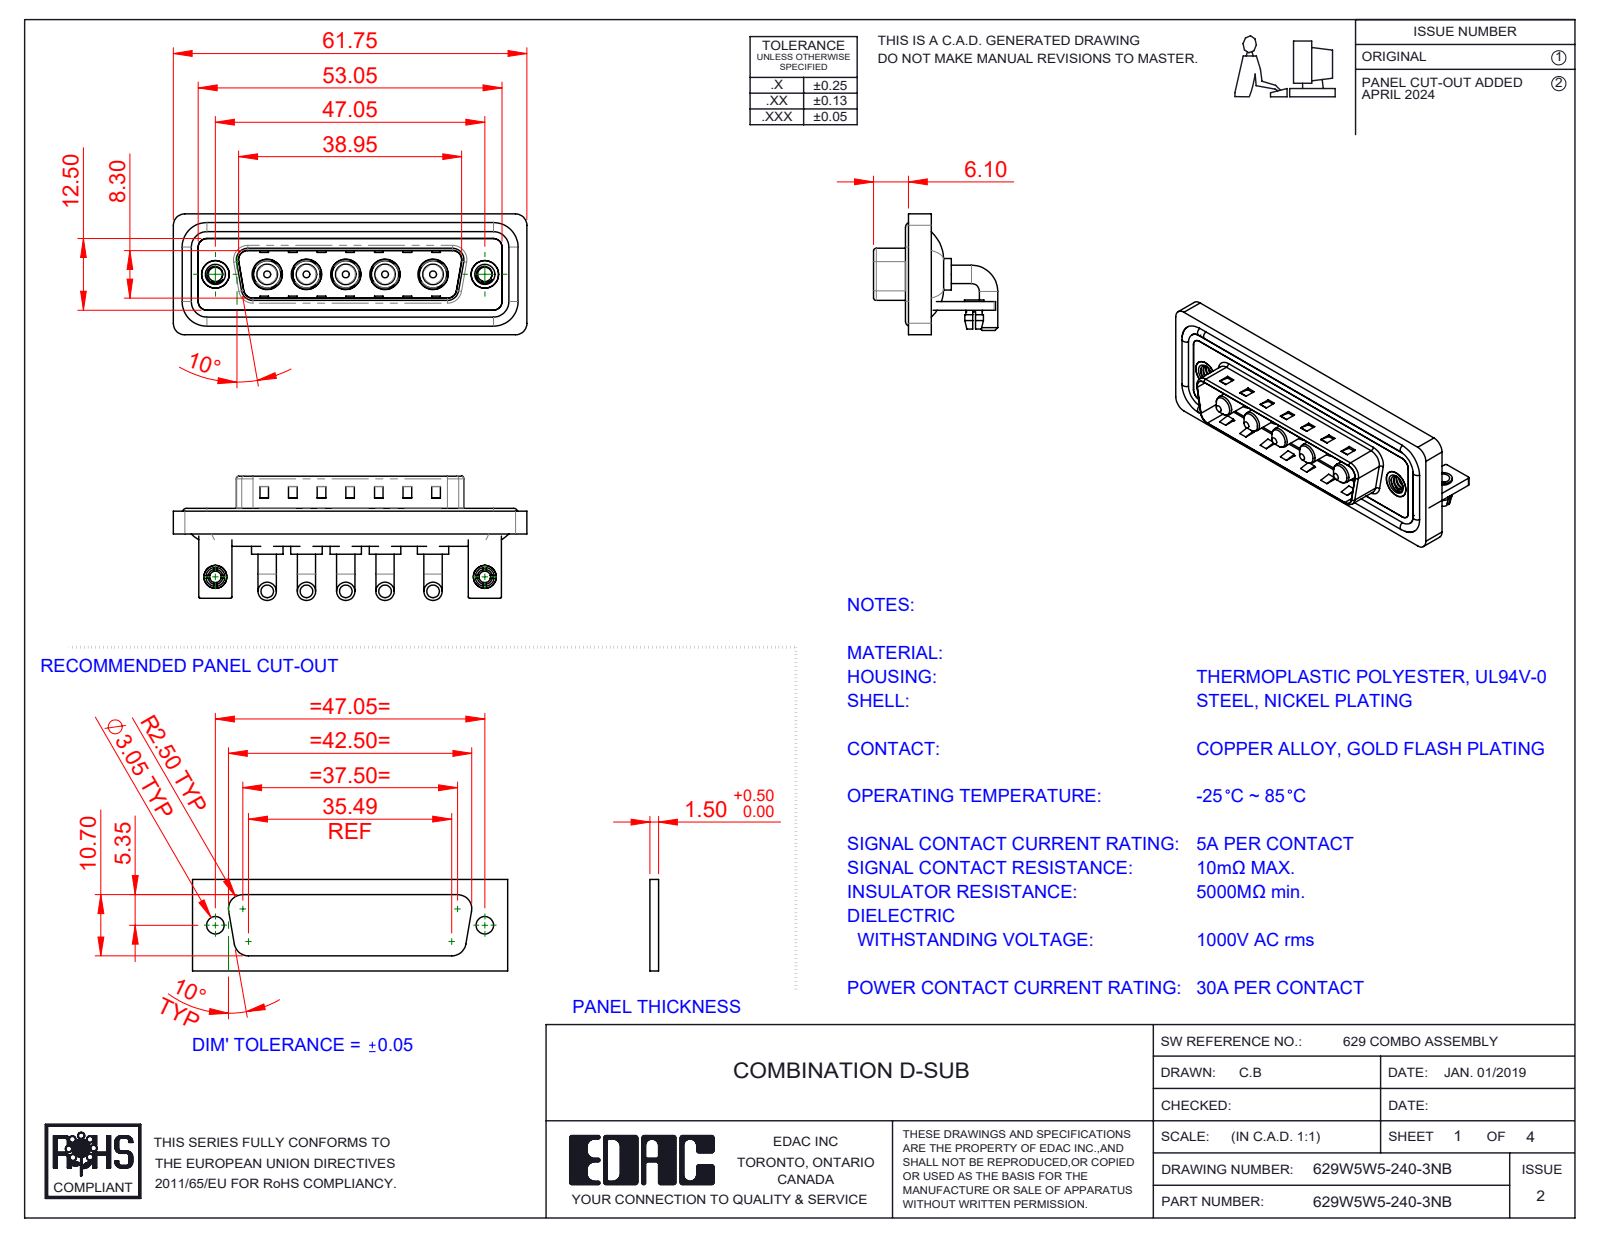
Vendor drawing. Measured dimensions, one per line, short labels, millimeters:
name: 629W5W5-140-3NB; Power Pin_30A RA; 629Combo Shell Front_25 Contacts; 629Combo Threaded Rivet_B (+5 more)
written by: SolidWorks 2023 (CONFIG_CONTROL_DESIGN)
unit: mm
bodies: 21 solids, 828 faces (327 planar, 343 cylindrical, 158 other)
size: 61.75 × 21.7 × 21.1
volume: 8 251 mm³; area: 13 163 mm²
holes: 5× ⌀4.85, 5× ⌀5.3, 4× ⌀2.5, 2× ⌀2, 2× ⌀3.2, 2× ⌀4, 2× ⌀4.8, 2× ⌀5
bosses: 10× ⌀3.2, 5× ⌀5.5, 5× ⌀5.2, 5× ⌀4.75, 5× ⌀3.75, 5× ⌀3.6, 4× ⌀1.6, 2× ⌀4.9
rounds: 19× R2, 18× R1.5, 16× R0.25, 9× R0.5, 8× R1.6, 5× R2.1, 4× R0.6, 4× R0.65
face distances: 0.4, 1.5, 2.9, 0.8, 2.1, 3.7, 1.1, 4.5, 4.1, 1.2
hole spacings: 6.86, 13.73, 47.05, 6.85, 6.87, 8.37, 8.38, 9.04
